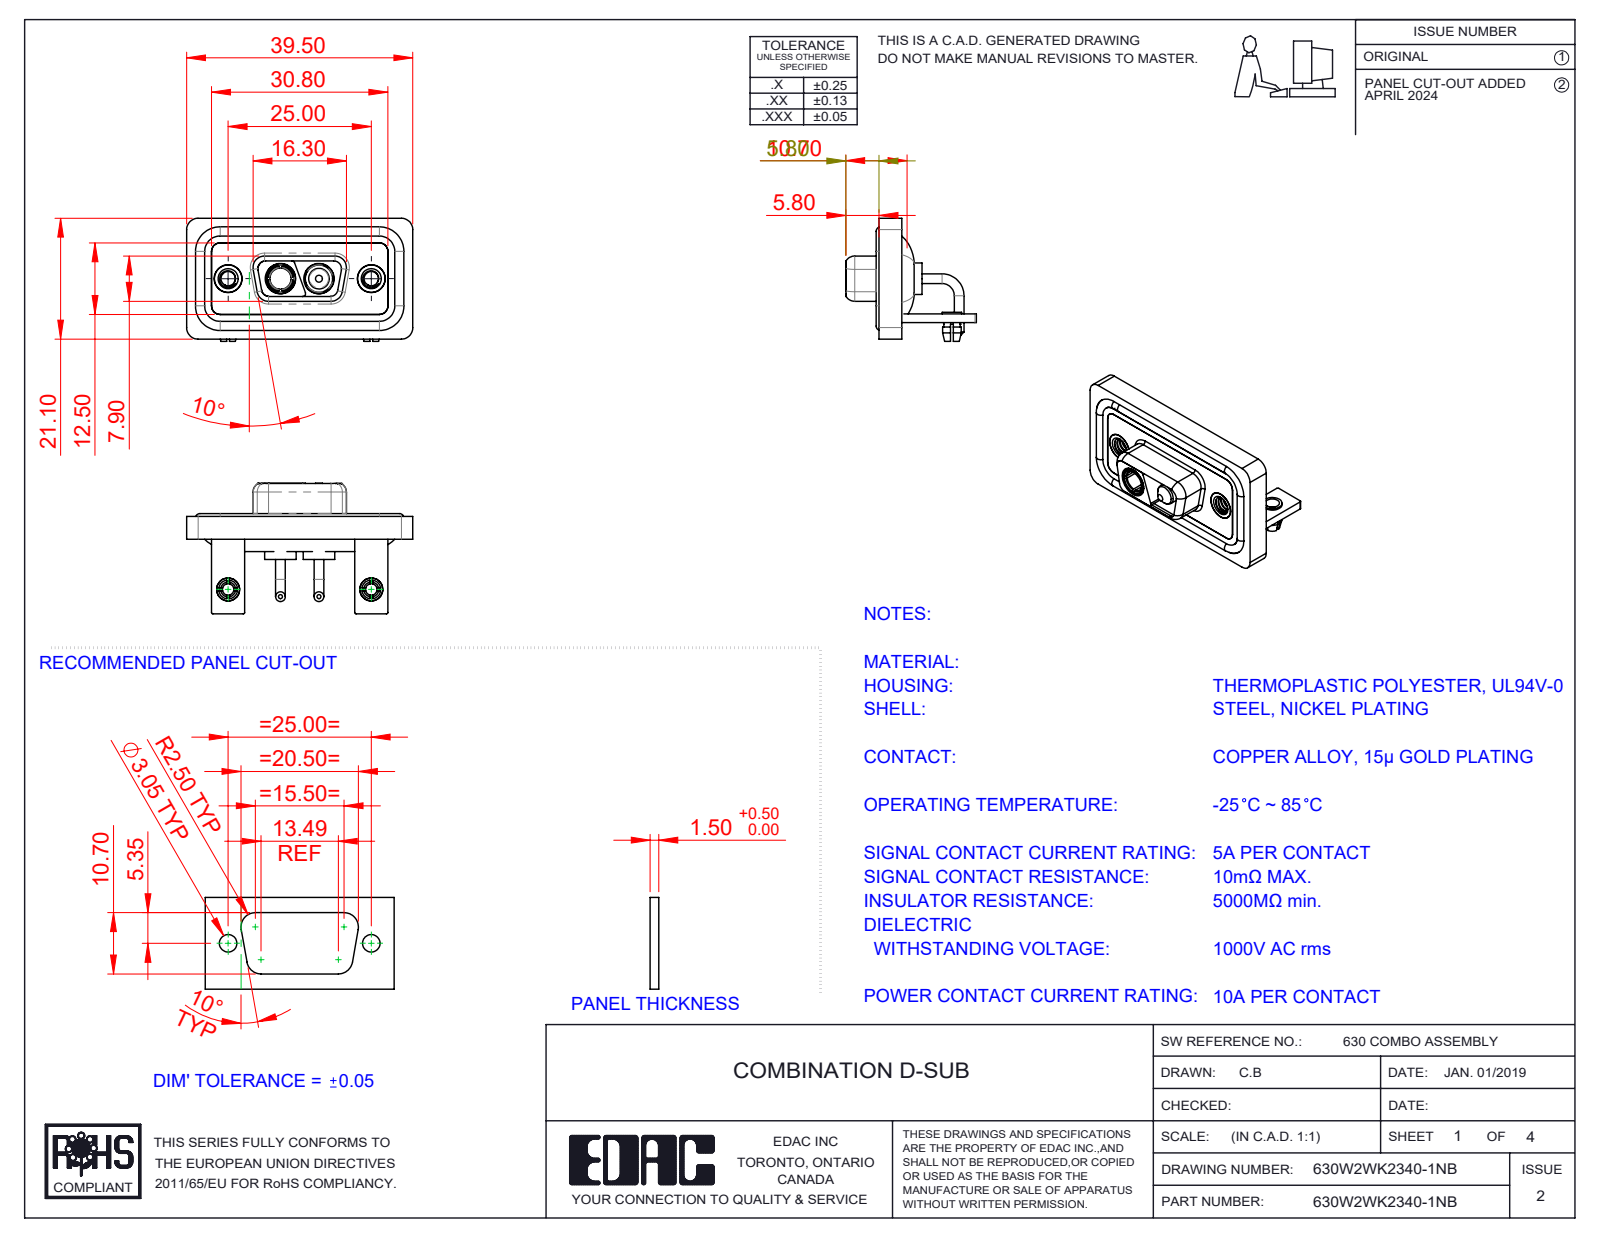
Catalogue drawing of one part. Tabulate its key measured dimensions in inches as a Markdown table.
| quantity | value |
| --- | --- |
| part name | 630Combo Housing_2WK2; Power Pin_10A RA; 630Combo Waterproof Housing_09 Contacts; 630Combo Board Lock_50 Contacts (+6 more) |
| STEP written by | SolidWorks 2023 (CONFIG_CONTROL_DESIGN) |
| units | inches |
| bodies | 15 solids, 642 faces (212 planar, 289 cylindrical, 141 other) |
| overall size | 1.555 × 0.898 × 0.846 |
| volume | 0.304 in³ |
| surface area | 12.93 in² |
| round holes (diameter × count) | 0.098 × 4, 0.191 × 4, 0.079 × 2, 0.126 × 2, 0.157 × 2, 0.159 × 2, 0.197 × 2, 0.209 × 2, 0.146 × 1 |
| round bosses / shafts (diameter × count) | 0.067 × 4, 0.063 × 4, 0.217 × 2, 0.205 × 2, 0.195 × 2, 0.189 × 2, 0.187 × 2, 0.157 × 2 |
| partial cylindrical surfaces (radius × count) | 0.079 × 19, 0.059 × 18, 0.01 × 16, 0.053 × 8, 0.063 × 8, 0.02 × 7, 0.024 × 4, 0.026 × 4 |
| main face-to-face distances | 0.016, 0.114, 0.059, 0.043, 0.146, 0.071, 0.031, 0.098, 0.063, 0.122 |
| hole center spacings | 0.36, 0.624, 0.984, 0.265 |
